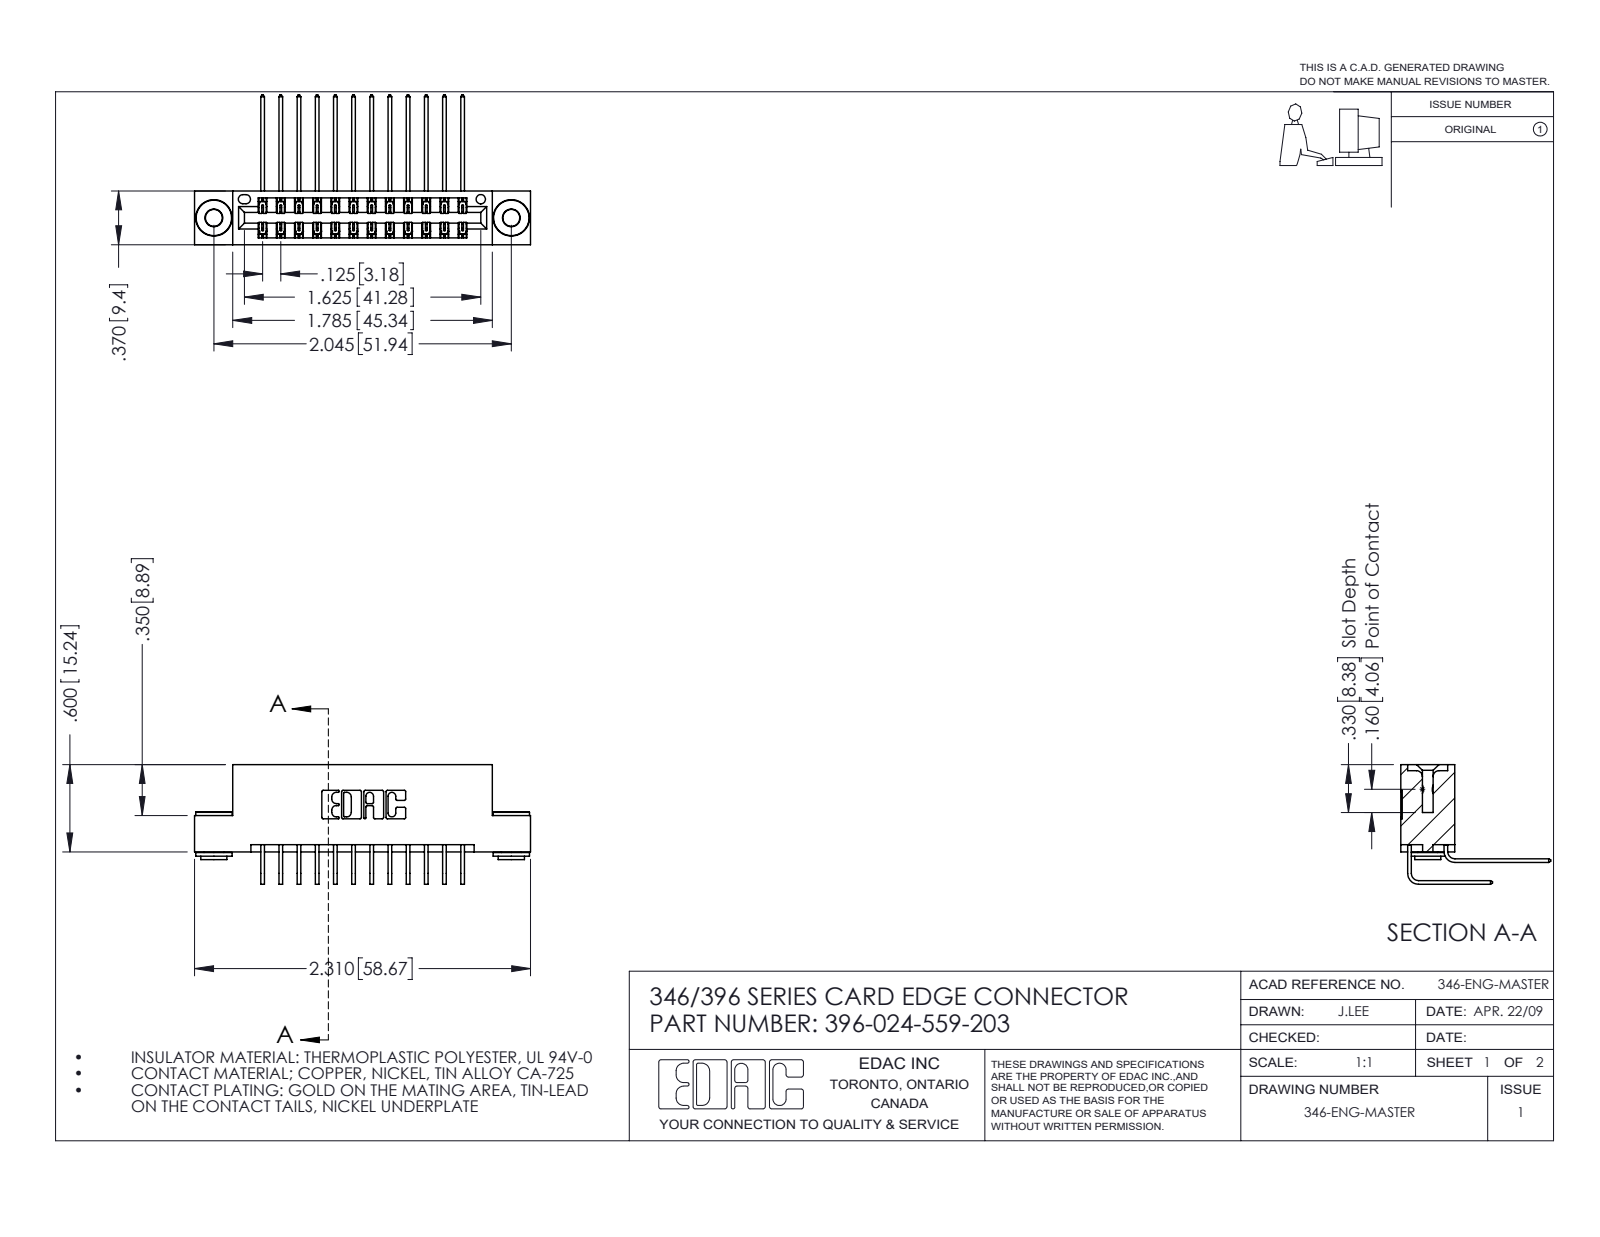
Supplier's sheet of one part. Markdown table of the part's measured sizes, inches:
| quantity | value |
| --- | --- |
| part name | 345-292-001_558 559 Tail - 1; 396-024-559-203; 345-250-002_345-250-002-102; 346 Part_Flush Mounting Lugs - 0.156 Dia-TH (+1 more) |
| STEP written by | SolidWorks 2016 (CONFIG_CONTROL_DESIGN) |
| units | inches |
| bodies | 27 solids, 1456 faces (974 planar, 474 cylindrical, 8 other) |
| overall size | 2.31 × 1.03 × 0.823 |
| volume | 0.345 in³ |
| surface area | 12.66 in² |
| round holes (diameter × count) | 0.116 × 2, 0.156 × 2, 0.064 × 1 |
| round bosses / shafts (diameter × count) | 0.25 × 2, 0.18 × 2, 0.136 × 2 |
| partial cylindrical surfaces (radius × count) | 0.006 × 36, 0.01 × 22, 0.007 × 6, 0.031 × 6, 0.026 × 3, 0.014 × 2, 0.022 × 2, 0.024 × 2 |
| main face-to-face distances | 0.048, 0.322, 0.25, 0.025, 0.37, 0.298, 0.072, 0.275, 0.148, 0.222 |
| hole center spacings | 0.246, 1.839, 2.045 |
